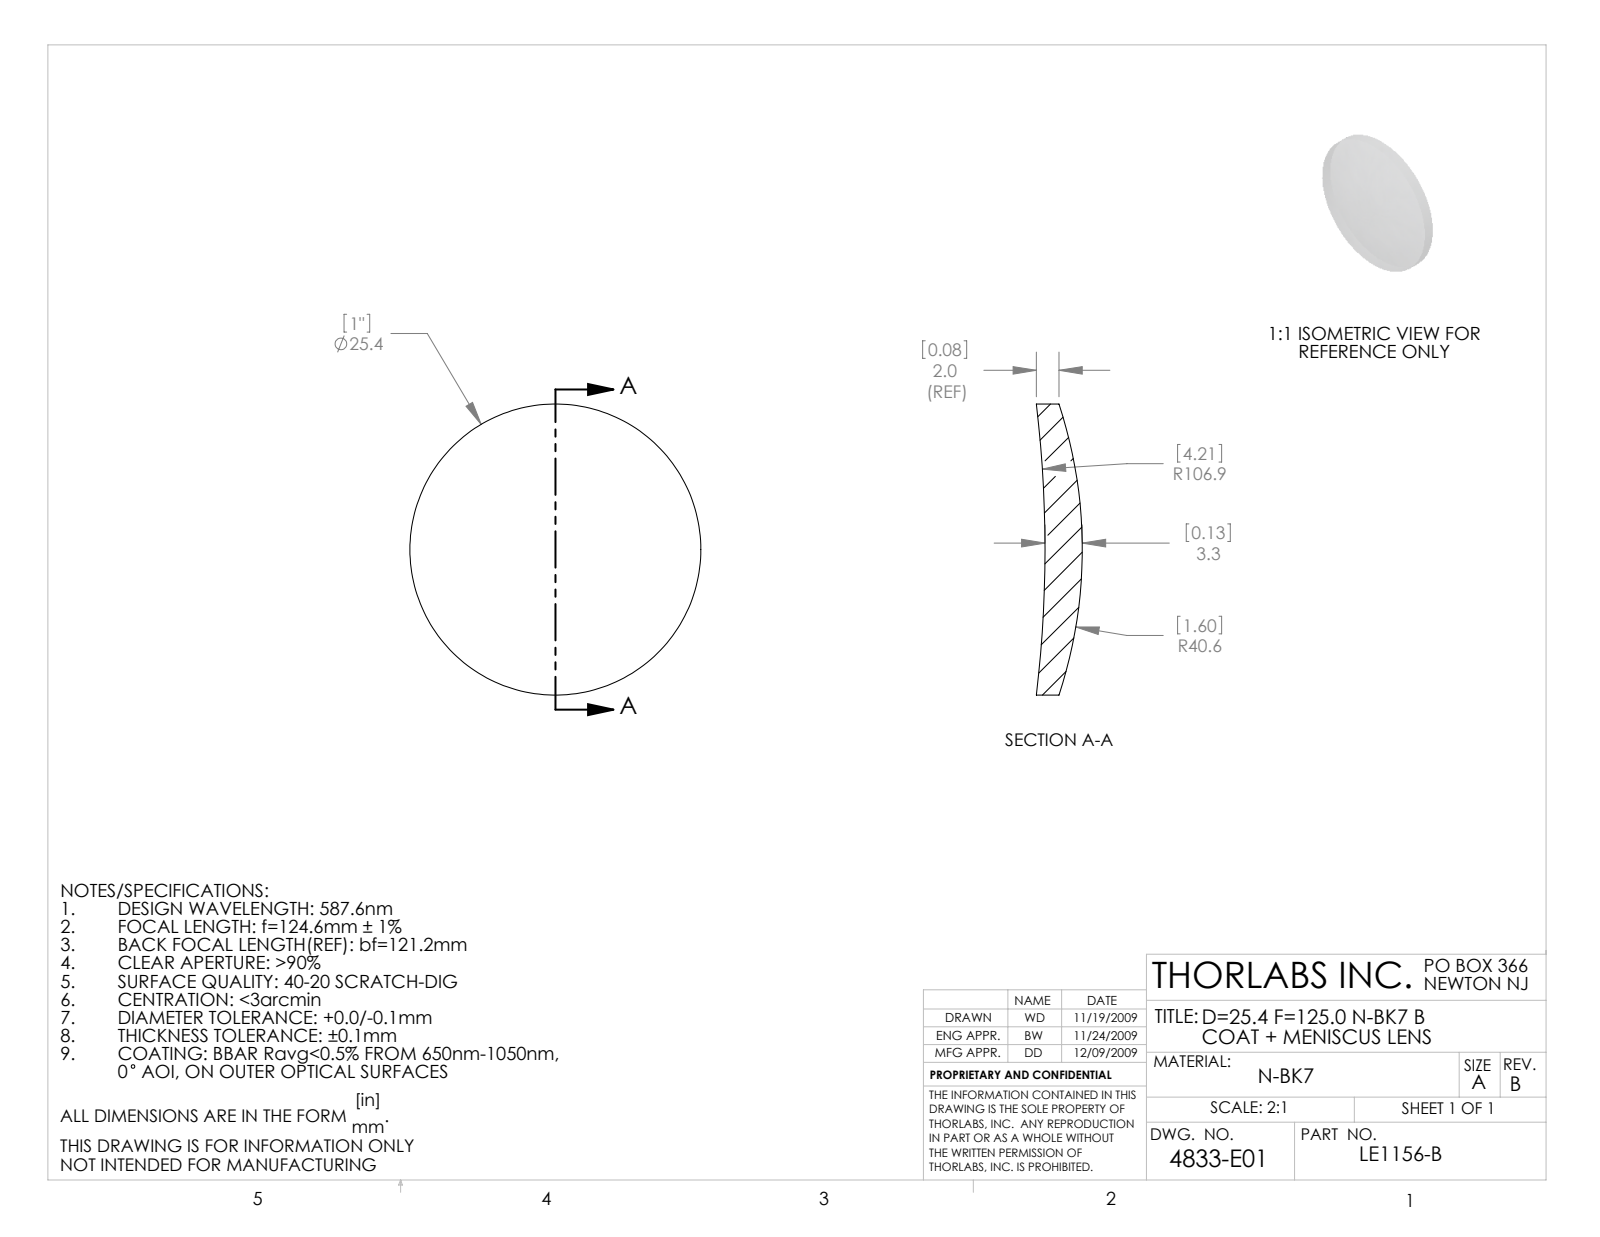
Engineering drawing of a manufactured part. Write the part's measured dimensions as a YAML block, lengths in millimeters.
part_name: "4833-E0W"
step_written_by: "SolidWorks 2009 (AUTOMOTIVE_DESIGN)"
units: millimeters
bodies: {solids: 1, faces: 6, planar: 0, cylindrical: 2, other: 4}
overall_size: [25.4, 25.4, 4.02]
volume: 1332
surface_area: 1186
round_bosses_or_shafts:
  - {diameter: 25.4, count: 1}
